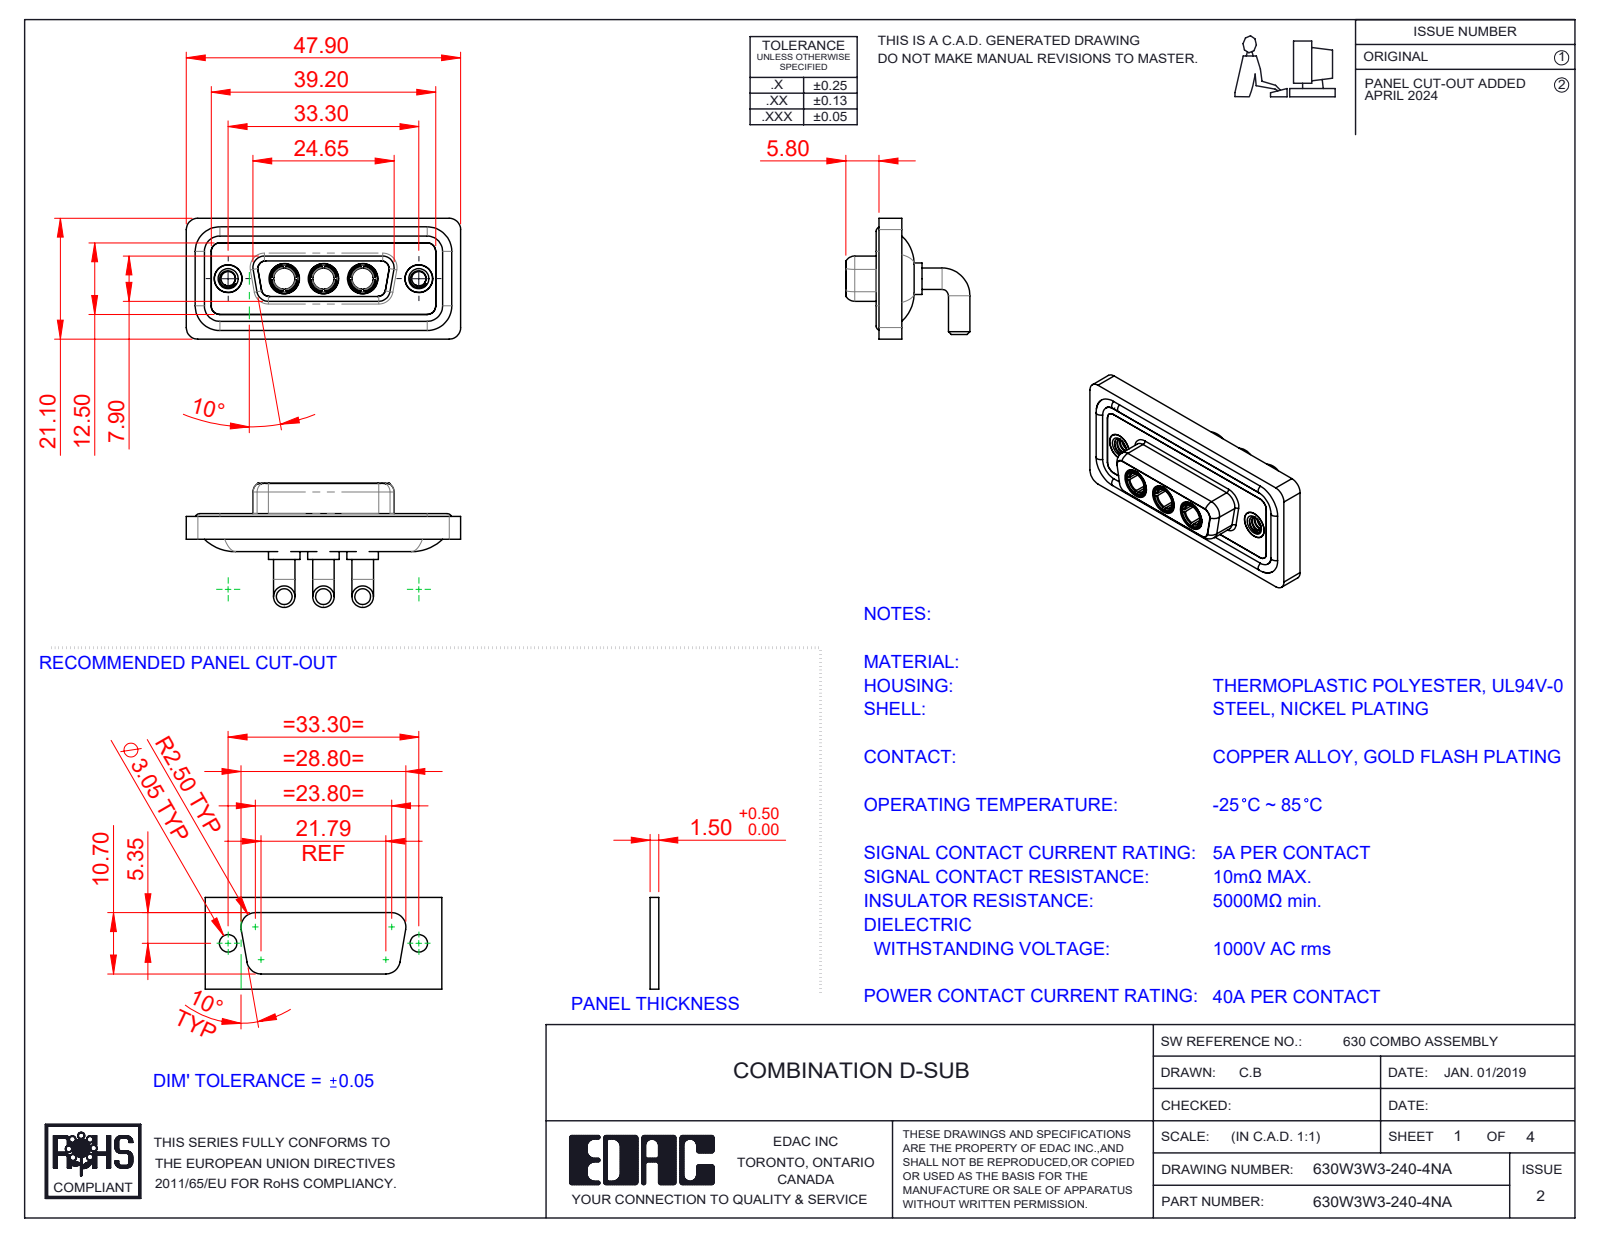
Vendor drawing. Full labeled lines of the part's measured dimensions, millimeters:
Part name (STEP PRODUCT): 630Combo Waterproof Housing_15 Contacts; 630W3W3-140-4NA; 630Combo Housing_3W3; Power Socket_40A RA (+3 more)
STEP written by: SolidWorks 2023 (CONFIG_CONTROL_DESIGN)
Units: millimetres
Bodies: 13 solids, 614 faces (192 planar, 261 cylindrical, 161 other)
Overall size (bounding box): 47.9 × 21.68 × 21.1
Volume: 6 391 mm³ · Surface area: 10 106 mm²
Round holes (diameter × count): ⌀4.85 ×5, ⌀3.7 ×3, ⌀5.3 ×3, ⌀2.5 ×2, ⌀4 ×2, ⌀4.05 ×2, ⌀5 ×2
Round bosses / shafts (diameter × count): ⌀3.75 ×6, ⌀1.6 ×4, ⌀5.5 ×3, ⌀5.2 ×3, ⌀4.96 ×3, ⌀4.75 ×3, ⌀4.95 ×2, ⌀4.8 ×2
Partial cylindrical surfaces — rounded edges, fillets, slot ends (radius × count): R2 ×20, R1.5 ×18, R1.35 ×12, R1.6 ×8, R0.25 ×4, R0.5 ×4, R0.6 ×4, R0.65 ×4
Main face-to-face distances: 0.4, 1.8, 1.1, 1.6, 2.9, 2.5, 3.1, 3.7, 4.1, 1.5
Hole centre spacings: 6.85, 9.8, 16.65, 23.5, 13.7, 33.3
